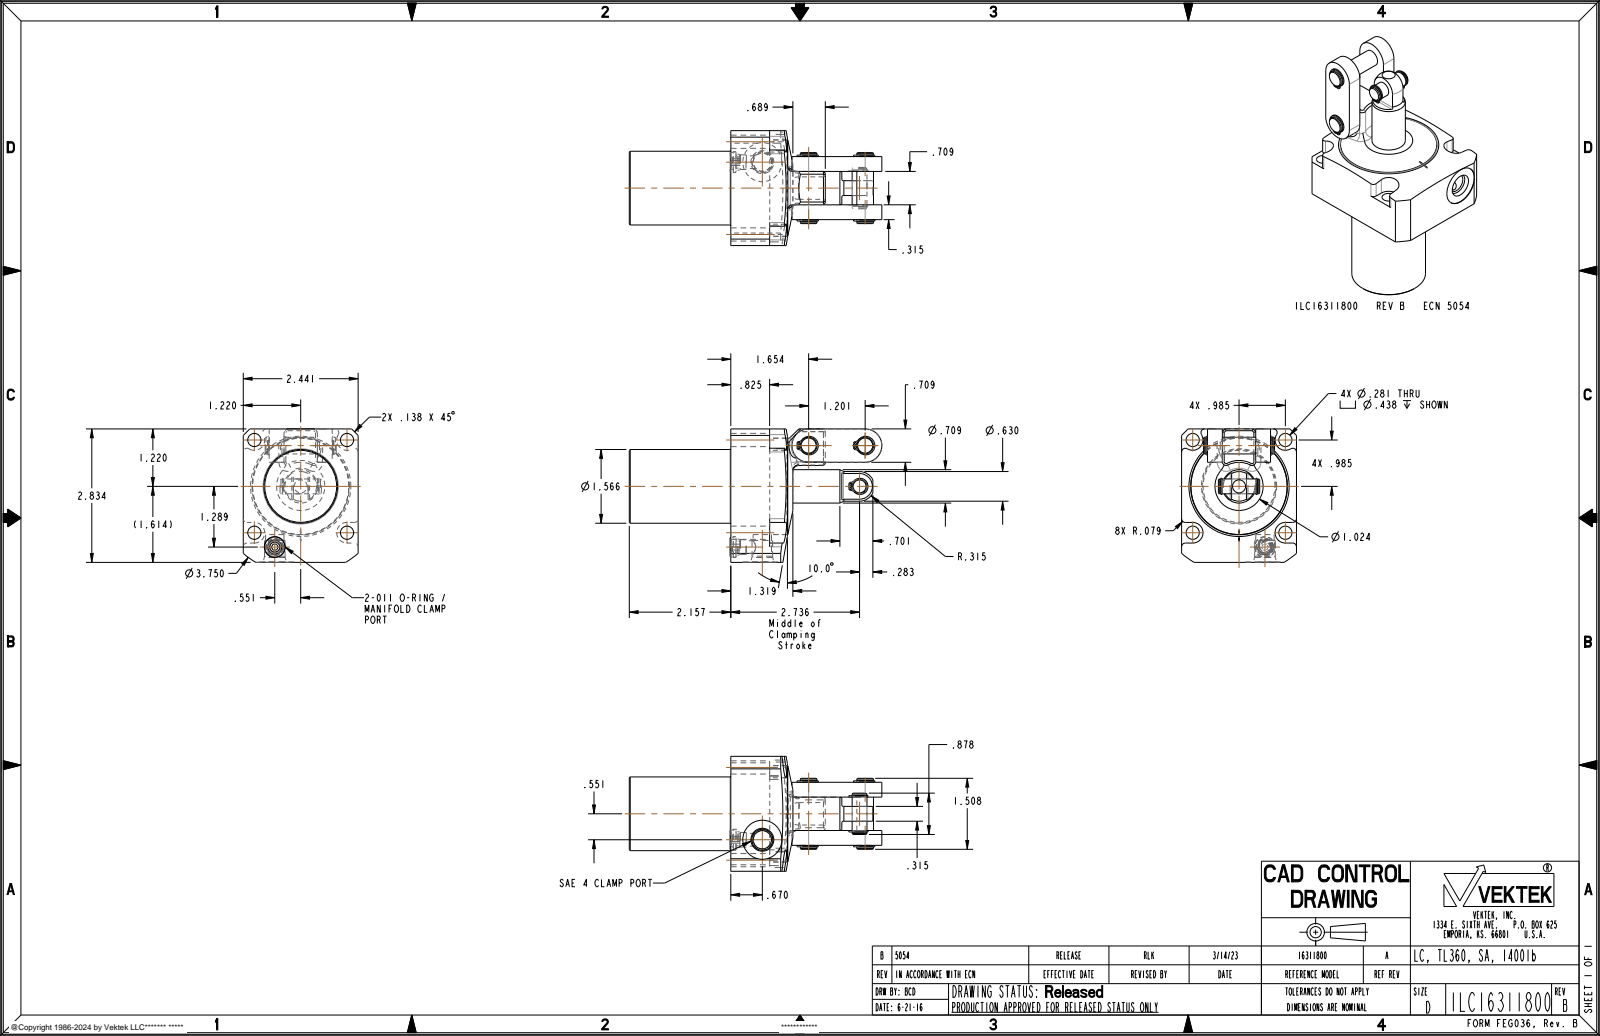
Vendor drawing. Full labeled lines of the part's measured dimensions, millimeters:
Part name (STEP PRODUCT): ILC16311800_BODY; ILC16311800_LUG; ILC16311800
STEP written by: CREO PARAMETRIC BY PTC INC, 2021164 (AUTOMOTIVE_DESIGN)
Units: millimetres
Bodies: 3 solids, 330 faces (114 planar, 155 cylindrical, 61 other)
Overall size (bounding box): 136.3 × 72 × 62
Volume: 225 600 mm³ · Surface area: 43 320 mm²
Round holes (diameter × count): ⌀1 ×6, ⌀7.1 ×4, ⌀6.9 ×1, ⌀8 ×1, ⌀9.9 ×1, ⌀11.3 ×1, ⌀21.1 ×1, ⌀52 ×1
Round bosses / shafts (diameter × count): ⌀10 ×2, ⌀9 ×2, ⌀8.4 ×2, ⌀51.9 ×1, ⌀39.8 ×1, ⌀18 ×1, ⌀11.1 ×1, ⌀10.9 ×1
Partial cylindrical surfaces — rounded edges, fillets, slot ends (radius × count): R2 ×10, R1 ×6, R0.8 ×4, R1.8 ×4, R5.6 ×4, R2.3 ×2, R9 ×2, R4.4 ×1
Main face-to-face distances: 21, 62, 14, 48, 54.8, 75.8, 22, 40, 8, 26
Hole centre spacings: 35.4, 50, 2.3, 4.9, 30.5, 30.6, 35.6, 70.7
